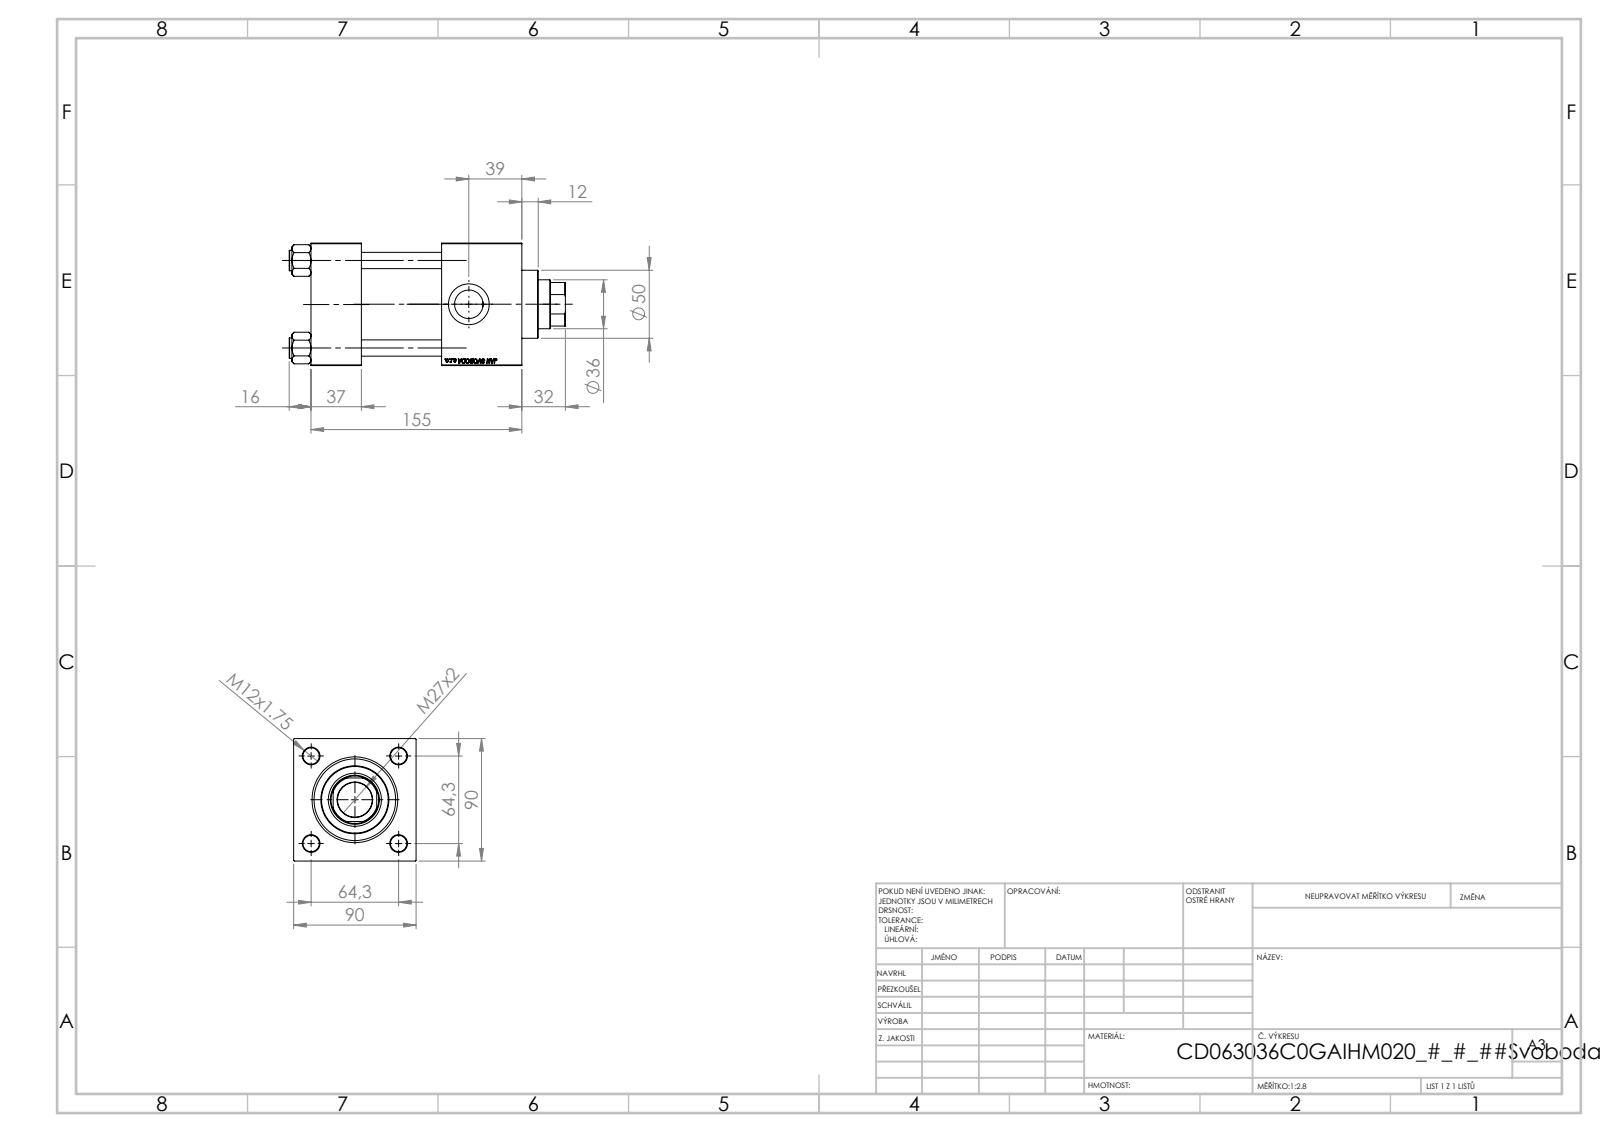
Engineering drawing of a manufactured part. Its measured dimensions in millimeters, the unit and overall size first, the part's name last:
Units: millimetres
Overall size (bounding box): 203 × 90 × 90
Round holes (diameter × count): ⌀12 ×4, ⌀7 ×2, ⌀20.96 ×2, ⌀30 ×2, ⌀25.5 ×1, ⌀36 ×1, ⌀39 ×1, ⌀50 ×1, ⌀60 ×1, ⌀63 ×1
Round bosses / shafts (diameter × count): ⌀15 ×4, ⌀69 ×1
Partial cylindrical surfaces — rounded edges, fillets, slot ends (radius × count): R17.5 ×1
Main face-to-face distances: 90, 59, 37, 155, 118, 96, 126.3, 89.3, 30.3, 28.7
Hole centre spacings: 45.47, 64.3, 90.93
Volume: 967 833 mm³ · Surface area: 184 238 mm²
Bodies: 11 solids, 1149 faces (526 planar, 87 cylindrical, 536 other)
Part name (STEP PRODUCT): V215CD_VC_C; V215CD_C_TYCINKA; V215CD_Body_C; NUT_M5_V215CD_C (+1 more)
STEP written by: SolidWorks 2019 (CONFIG_CONTROL_DESIGN)
